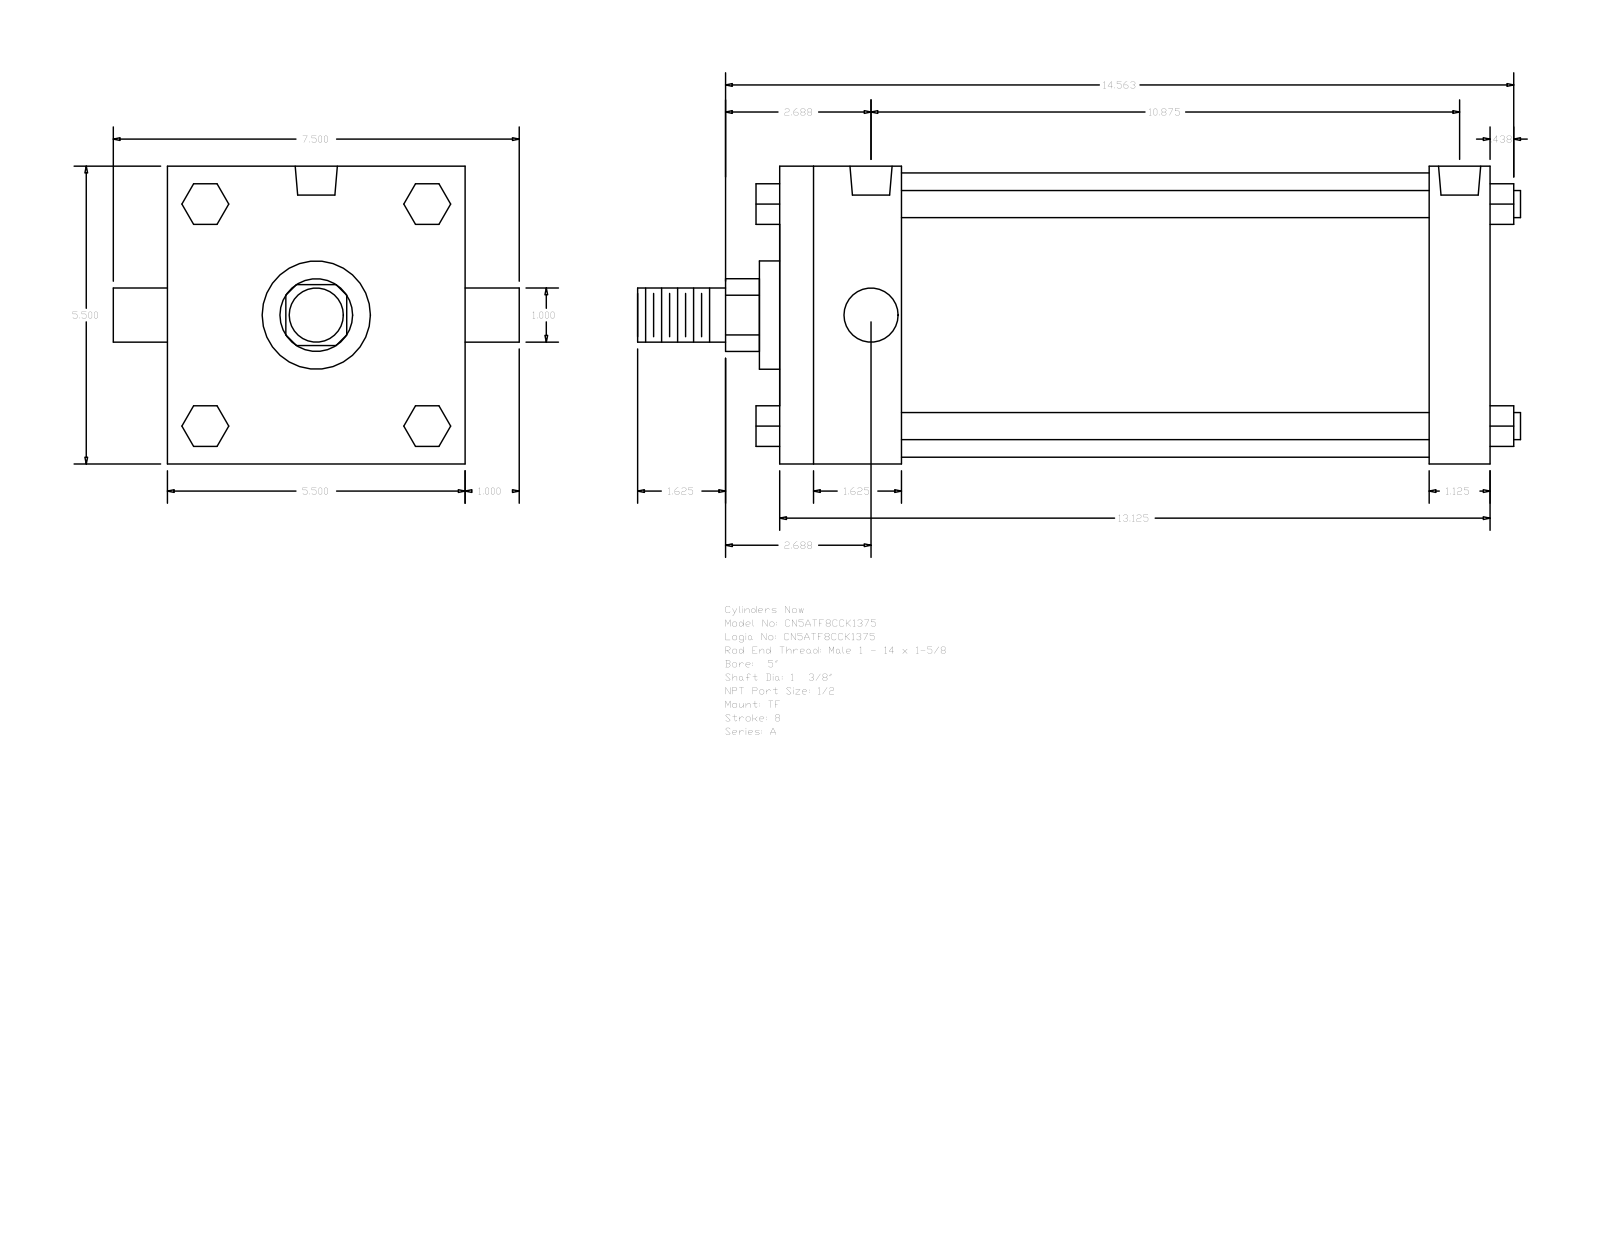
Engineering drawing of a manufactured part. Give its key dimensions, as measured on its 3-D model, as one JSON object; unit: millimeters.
{"part_name": "A_TF__0500_1.375", "step_written_by": "GSSL Pune (CONFIG_CONTROL_DESIGN)", "units": "millimeters", "bodies": {"solids": 0, "faces": 120, "planar": 92, "cylindrical": 28, "other": 0}, "overall_size": [414.34, 190.5, 139.7], "round_holes": [[8.73, 3], [19.77, 2]], "round_bosses_or_shafts": [[12.7, 4], [25.4, 2], [133.35, 1], [50.8, 1], [34.92, 1]], "partial_cylinders_radius": [[17.06, 1]], "face_to_face_distances": [139.7, 333.37, 57.15, 304.8, 28.57, 247.65, 276.22, 19.05, 52.07, 90.18], "hole_center_spacings": [2.39, 273.84, 271.45, 276.23]}
